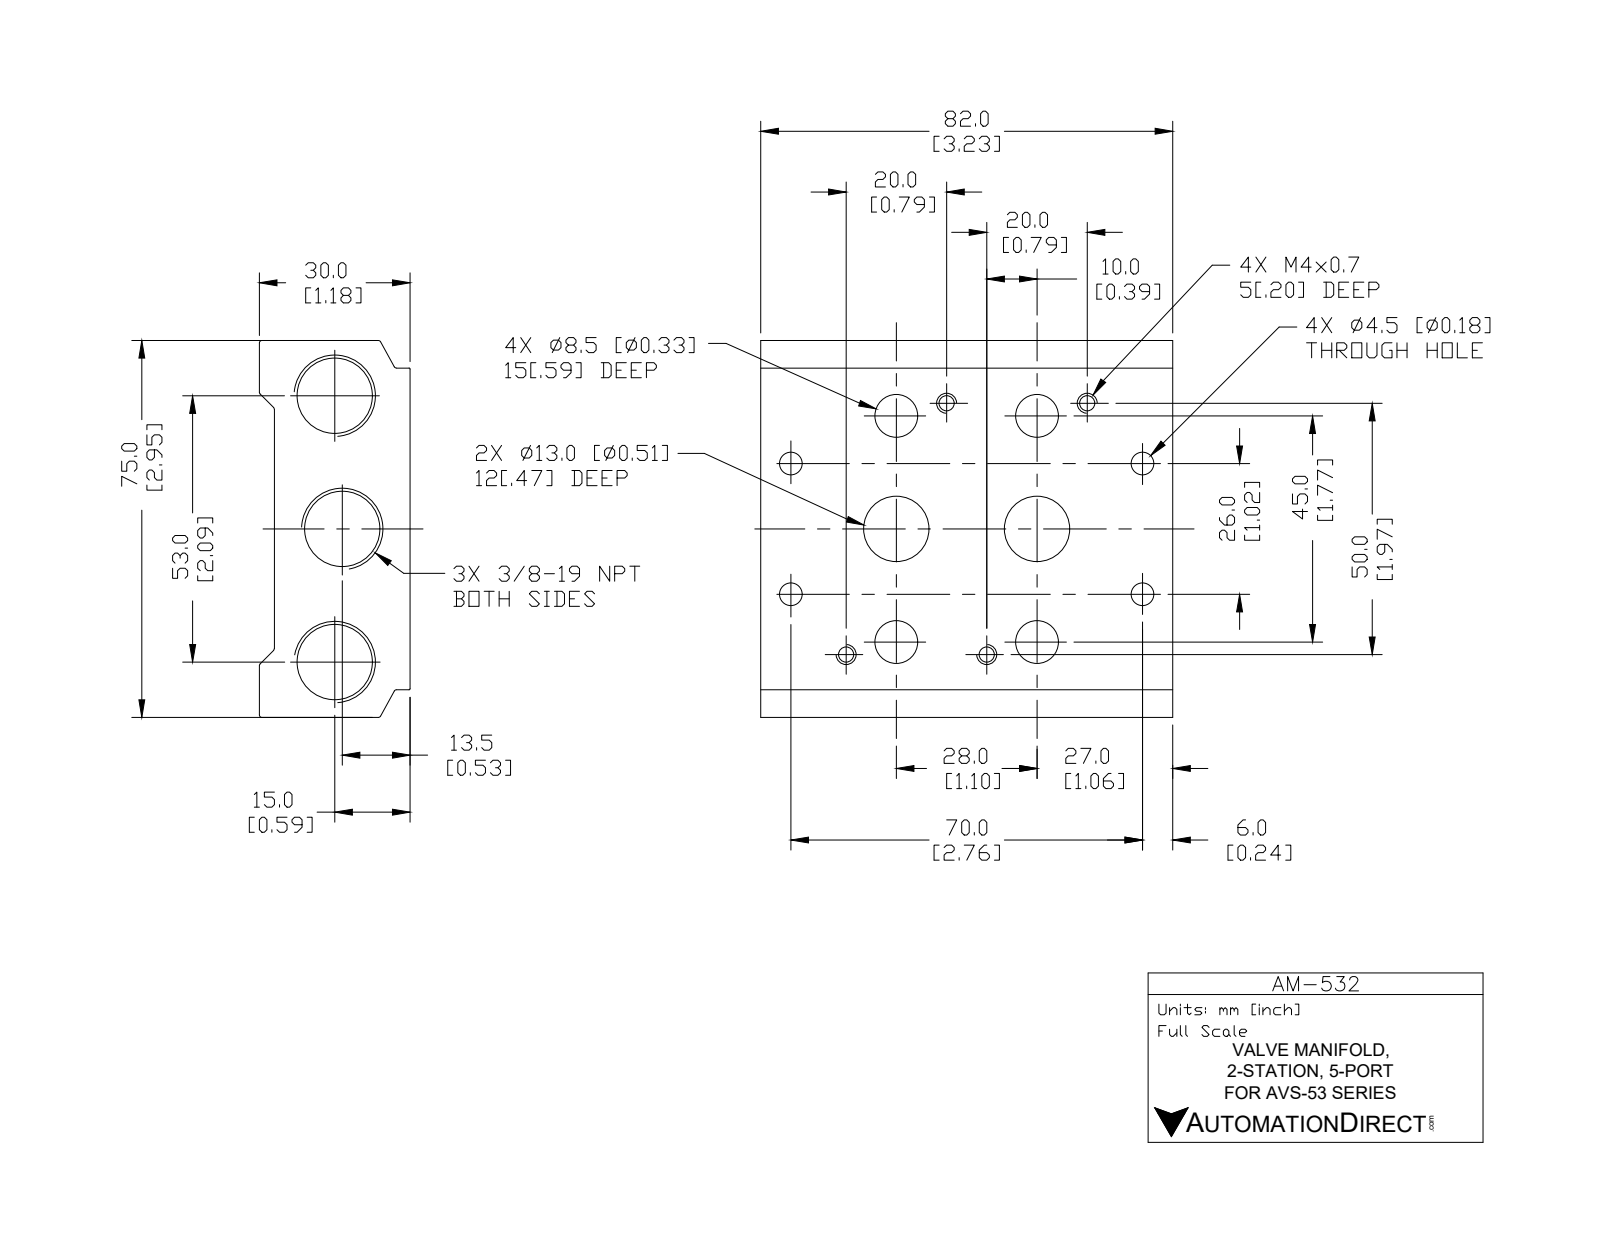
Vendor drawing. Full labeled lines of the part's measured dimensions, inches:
Part name (STEP PRODUCT): AM-532
STEP written by: SolidWorks 2019 (CONFIG_CONTROL_DESIGN)
Units: inches
Bodies: 1 solid, 93 faces (28 planar, 45 cylindrical, 20 other)
Overall size (bounding box): 3.228 × 2.953 × 1.181
Volume: 7.33 in³ · Surface area: 52.87 in²
Round holes (diameter × count): ⌀0.13 ×4, ⌀0.177 ×4, ⌀0.335 ×4, ⌀0.562 ×3, ⌀0.512 ×2
Partial cylindrical surfaces — rounded edges, fillets, slot ends (radius × count): R0.02 ×11
Main face-to-face distances: 1.063, 2.953, 0.118, 1.181, 3.228, 0.407, 2.822, 0.236, 2.717, 2.415
Hole centre spacings: 1.102, 0.406, 0.886, 0.907, 0.972, 1.06, 1.414, 1.624
